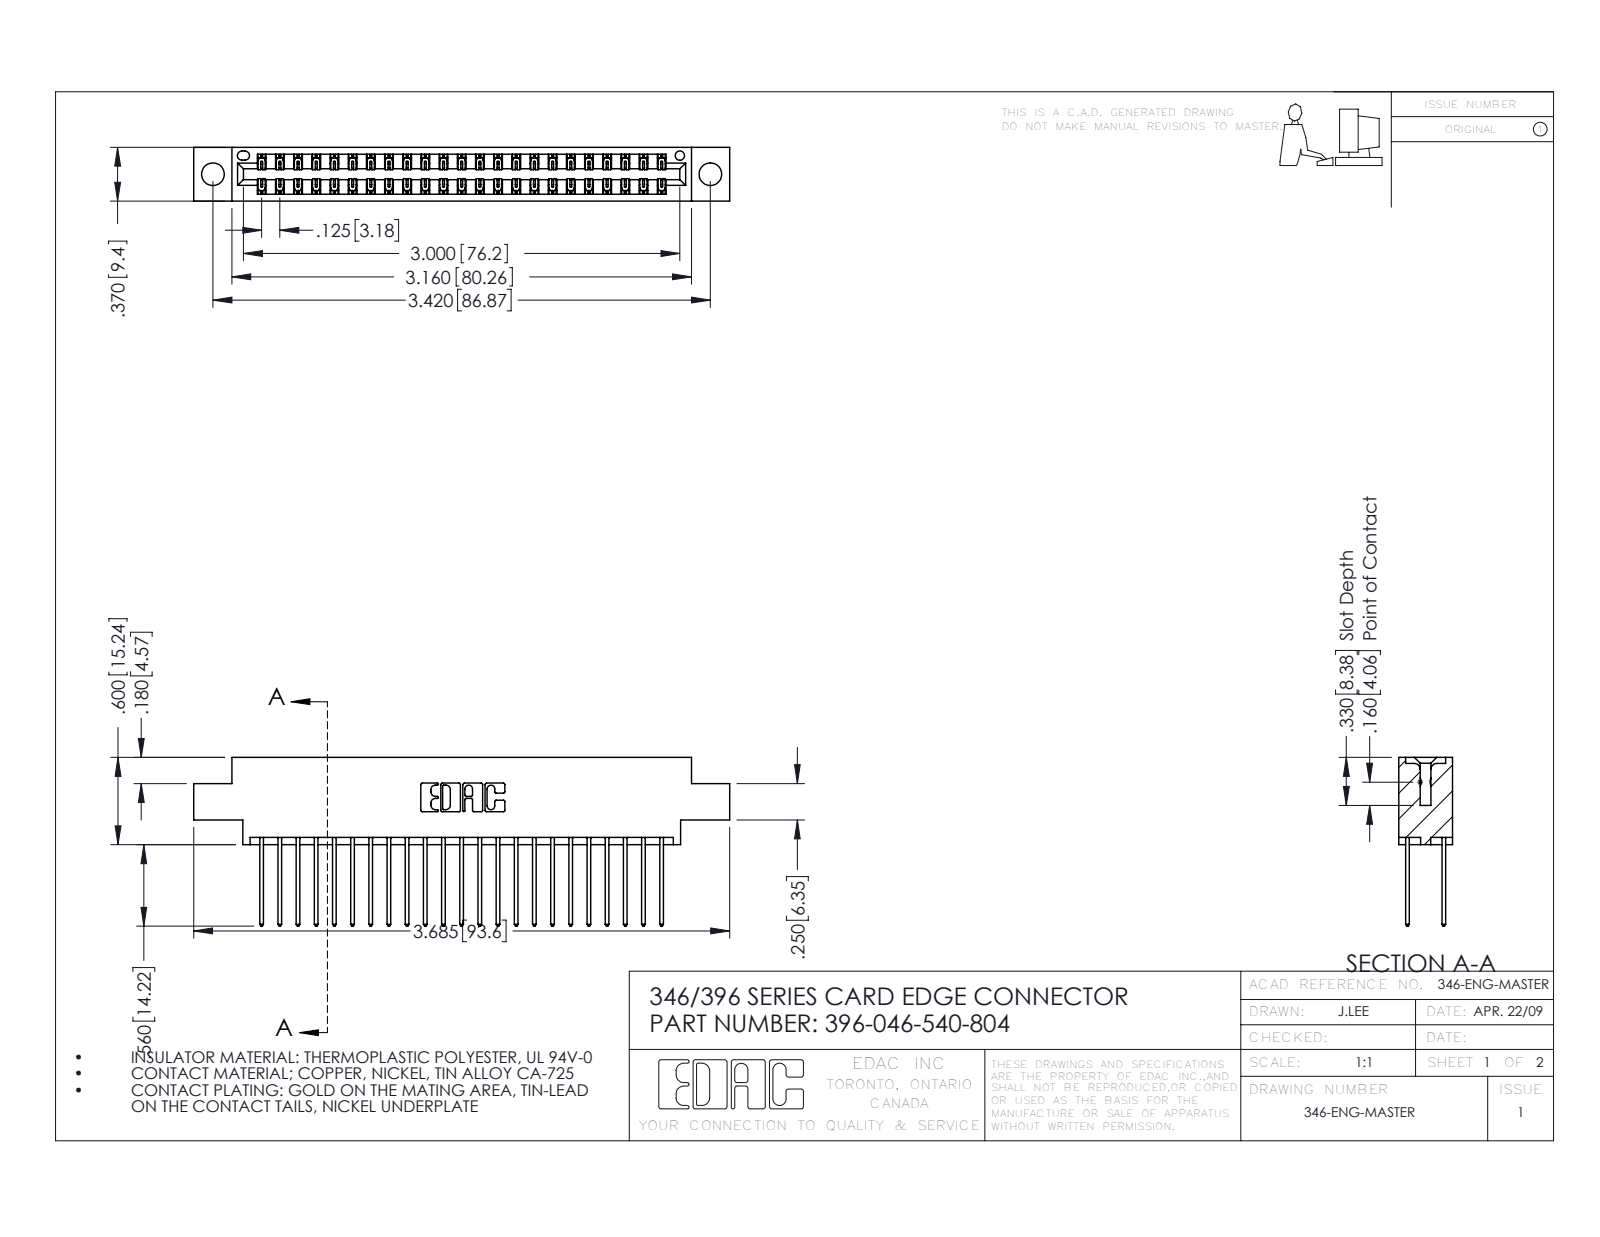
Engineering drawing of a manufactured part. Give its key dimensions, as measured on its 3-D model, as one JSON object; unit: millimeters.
{"part_name": "345-292-001_345-293-140; 396-046-540-804; 346 Part_0.170 Offset - 0.156 Dia-TH", "step_written_by": "SolidWorks 2016 (CONFIG_CONTROL_DESIGN)", "units": "millimeters", "bodies": {"solids": 47, "faces": 2518, "planar": 1690, "cylindrical": 828, "other": 0}, "overall_size": [93.6, 29.5, 9.4], "volume_mm3": 8910, "surface_area_mm2": 12770, "round_holes": [[4, 2], [1.6, 1]], "partial_cylinders_radius": [[0.2, 69], [0.3, 46], [0.3, 22], [0.2, 6], [0.8, 6], [0.7, 3], [0.4, 2], [0.6, 2]], "face_to_face_distances": [1.2, 8.2, 6.4, 9.4, 1.8, 7.6, 0.6, 7, 3.8, 5.6], "hole_center_spacings": [6.2, 81.6, 86.9]}
